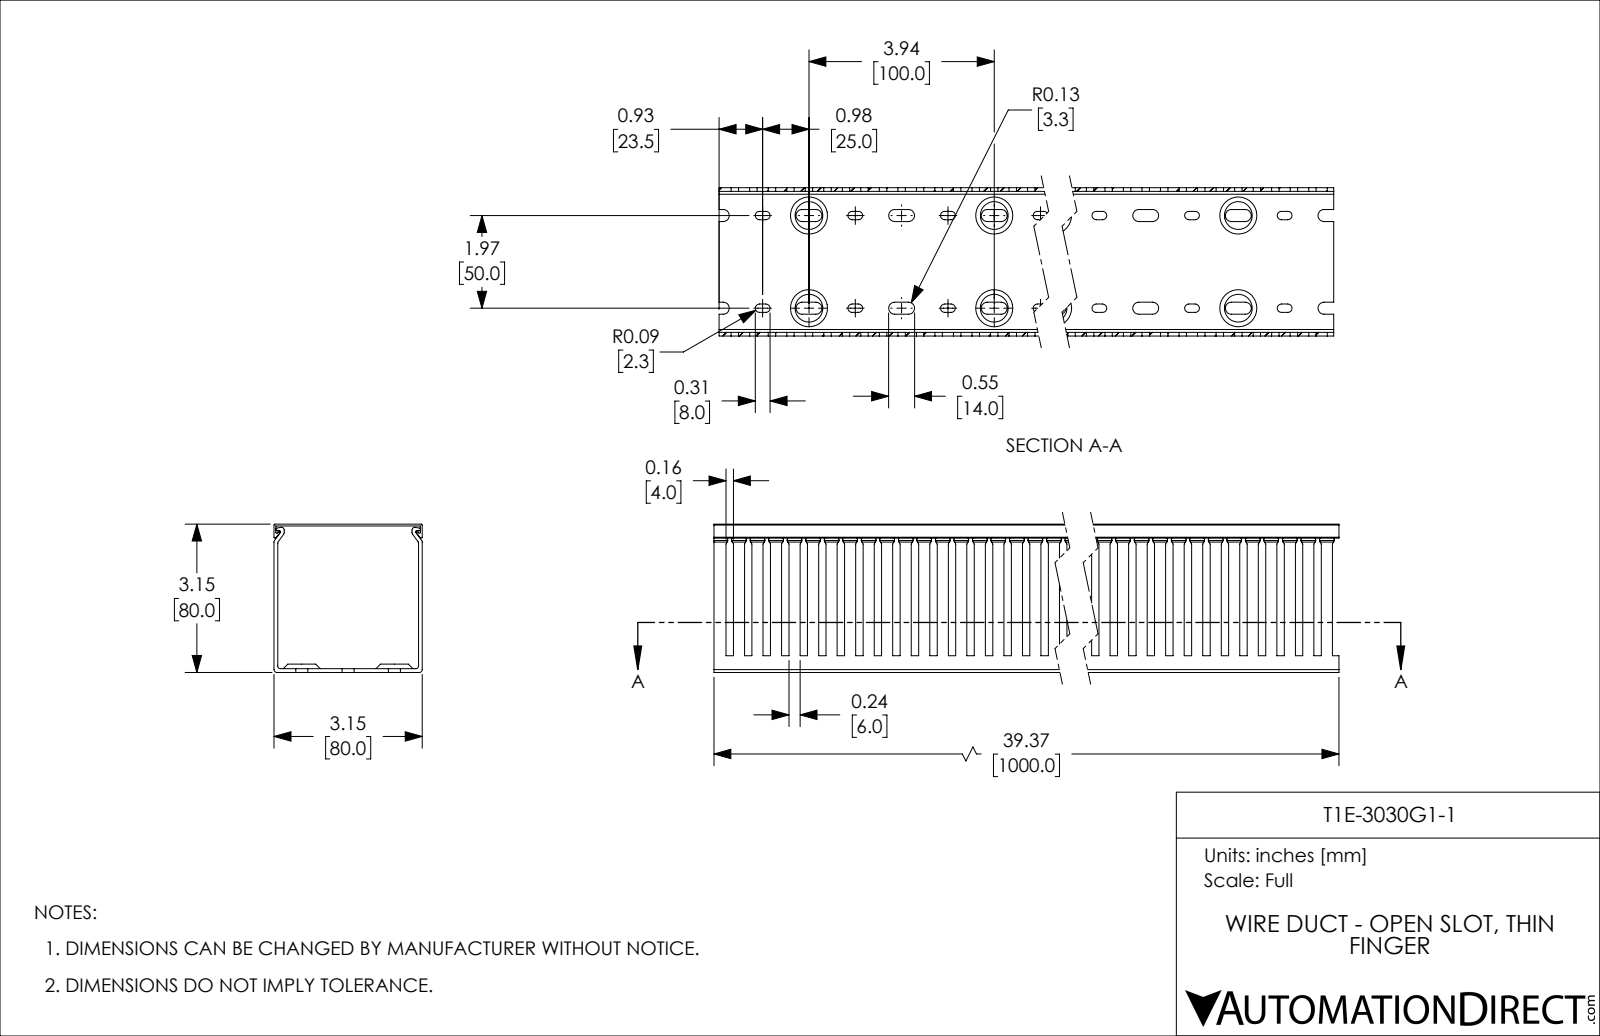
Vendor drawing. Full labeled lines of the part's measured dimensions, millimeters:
Part name (STEP PRODUCT): T1E-3030G1-1
STEP written by: SolidWorks 2021 (CONFIG_CONTROL_DESIGN)
Units: millimetres
Bodies: 2 solids, 1063 faces (562 planar, 461 cylindrical, 40 other)
Overall size (bounding box): 1000 × 80 × 80
Volume: 561 393 mm³ · Surface area: 664 587 mm²
Partial cylindrical surfaces — rounded edges, fillets, slot ends (radius × count): R3.25 ×100, R2.25 ×80, R1.5 ×12, R0.5 ×8, R0.75 ×6
Main face-to-face distances: 2, 78, 80, 1, 79, 77, 76, 4.5, 74.5, 10
